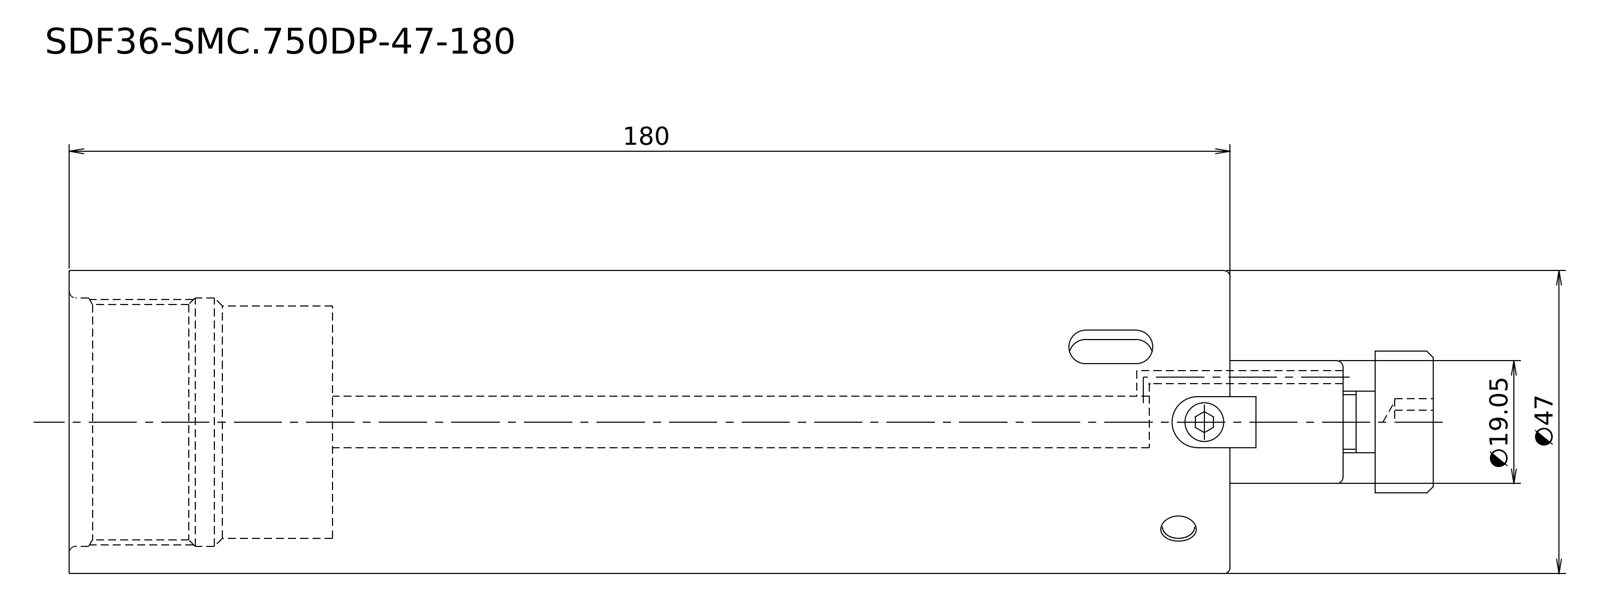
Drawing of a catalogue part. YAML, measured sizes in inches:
step_written_by: "Kubotek KeyCreator 2011 V10.0.2 (22737) (automotive_design)"
units: inches
bodies: {solids: 1, faces: 5, planar: 3, cylindrical: 2, other: 0}
overall_size: [7.776, 1.85, 1.85]
volume: 19.36
surface_area: 48.2
round_bosses_or_shafts:
  - {diameter: 1.85, count: 1}
  - {diameter: 0.75, count: 1}
face_to_face_distances: [7.087, 0.689, 7.776]
